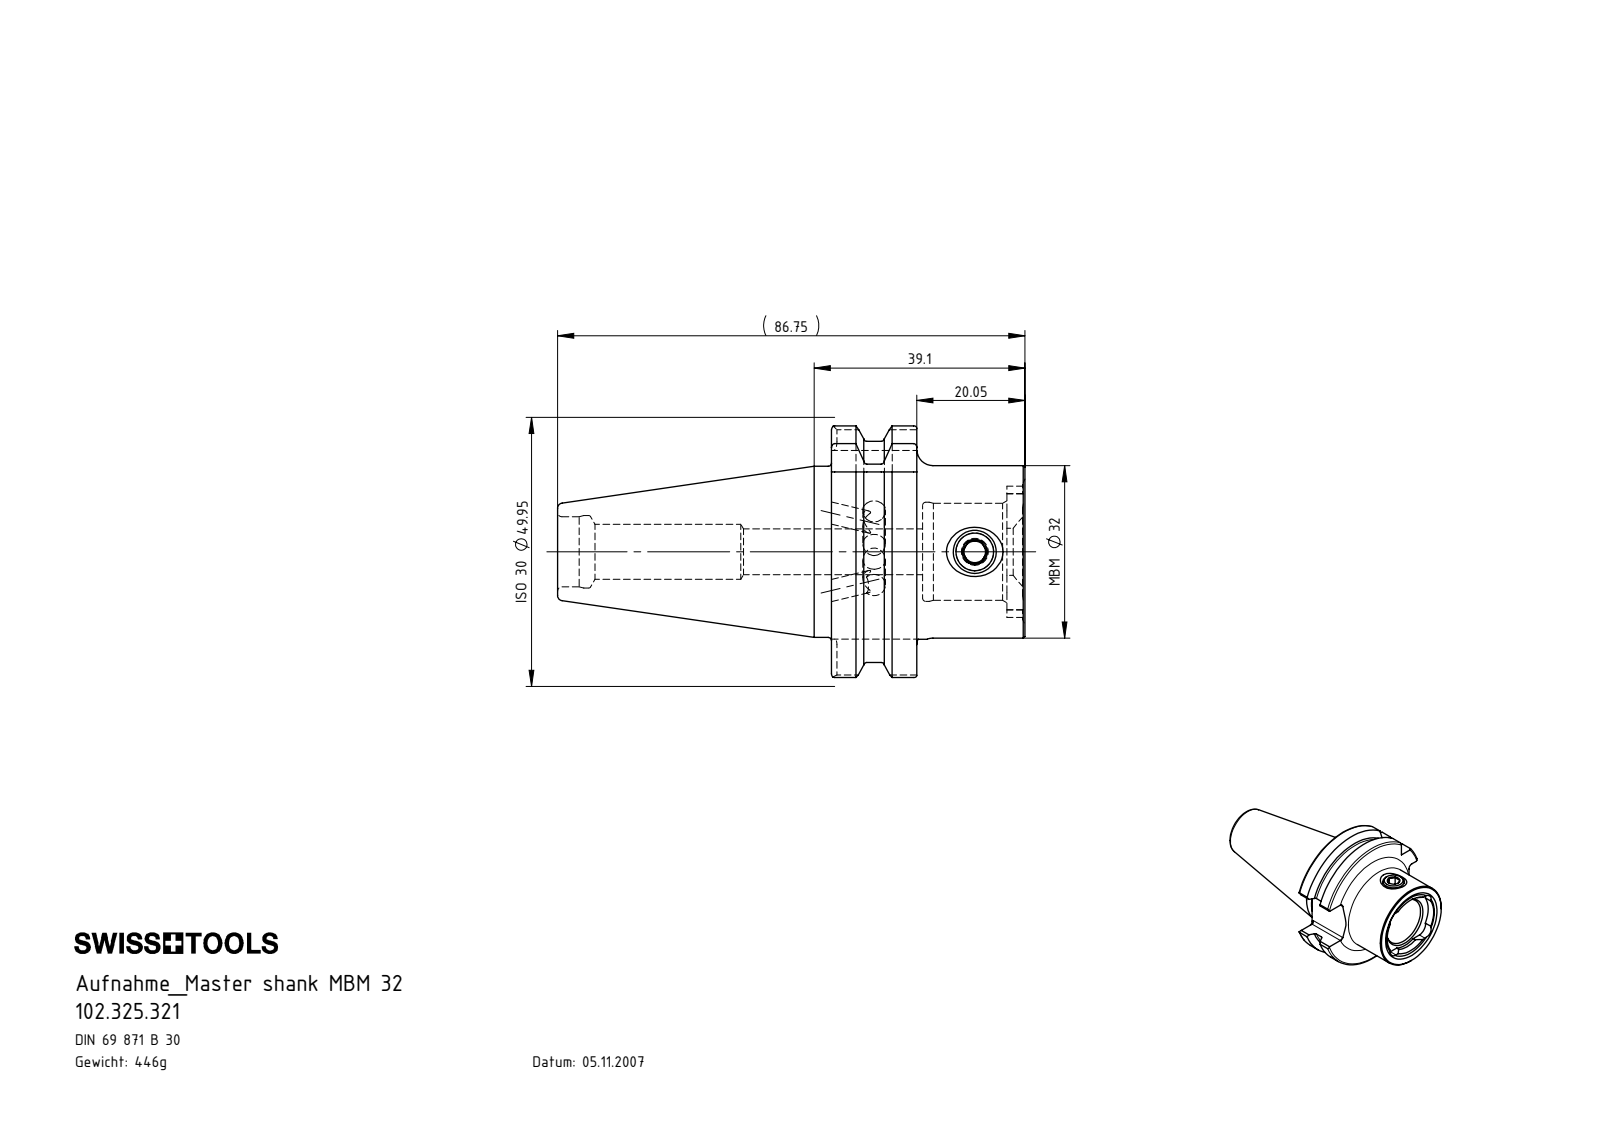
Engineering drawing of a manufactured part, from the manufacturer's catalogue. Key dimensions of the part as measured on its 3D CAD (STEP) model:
Part name (STEP PRODUCT): 102.325.321; MB3-ER1.001.011_A; SB3-MB3.K01.039_C_mit Bundkhlung
STEP written by: SolidWorks 2017 (CONFIG_CONTROL_DESIGN)
Units: millimetres
Bodies: 2 solids, 183 faces (50 planar, 61 cylindrical, 72 other)
Overall size (bounding box): 86.75 × 49.95 × 46.69
Volume: 56 871 mm³ · Surface area: 15 729 mm²
Round holes (diameter × count): ⌀4 ×3, ⌀4.2 ×1, ⌀7 ×1, ⌀8.5 ×1, ⌀10.2 ×1, ⌀13 ×1, ⌀13.45 ×1, ⌀18 ×1, ⌀18.4 ×1
Round bosses / shafts (diameter × count): ⌀32 ×1, ⌀31.75 ×1, ⌀8 ×1
Partial cylindrical surfaces — rounded edges, fillets, slot ends (radius × count): R1 ×4, R1.6 ×4, R3.2 ×4, R8.05 ×1, R10.5 ×1, R12.18 ×1, R22.02 ×1, R24.98 ×1
Main face-to-face distances: 15.85, 35, 35.9, 20.05, 16.9, 1.05, 19, 3.35, 32.55, 16.7
